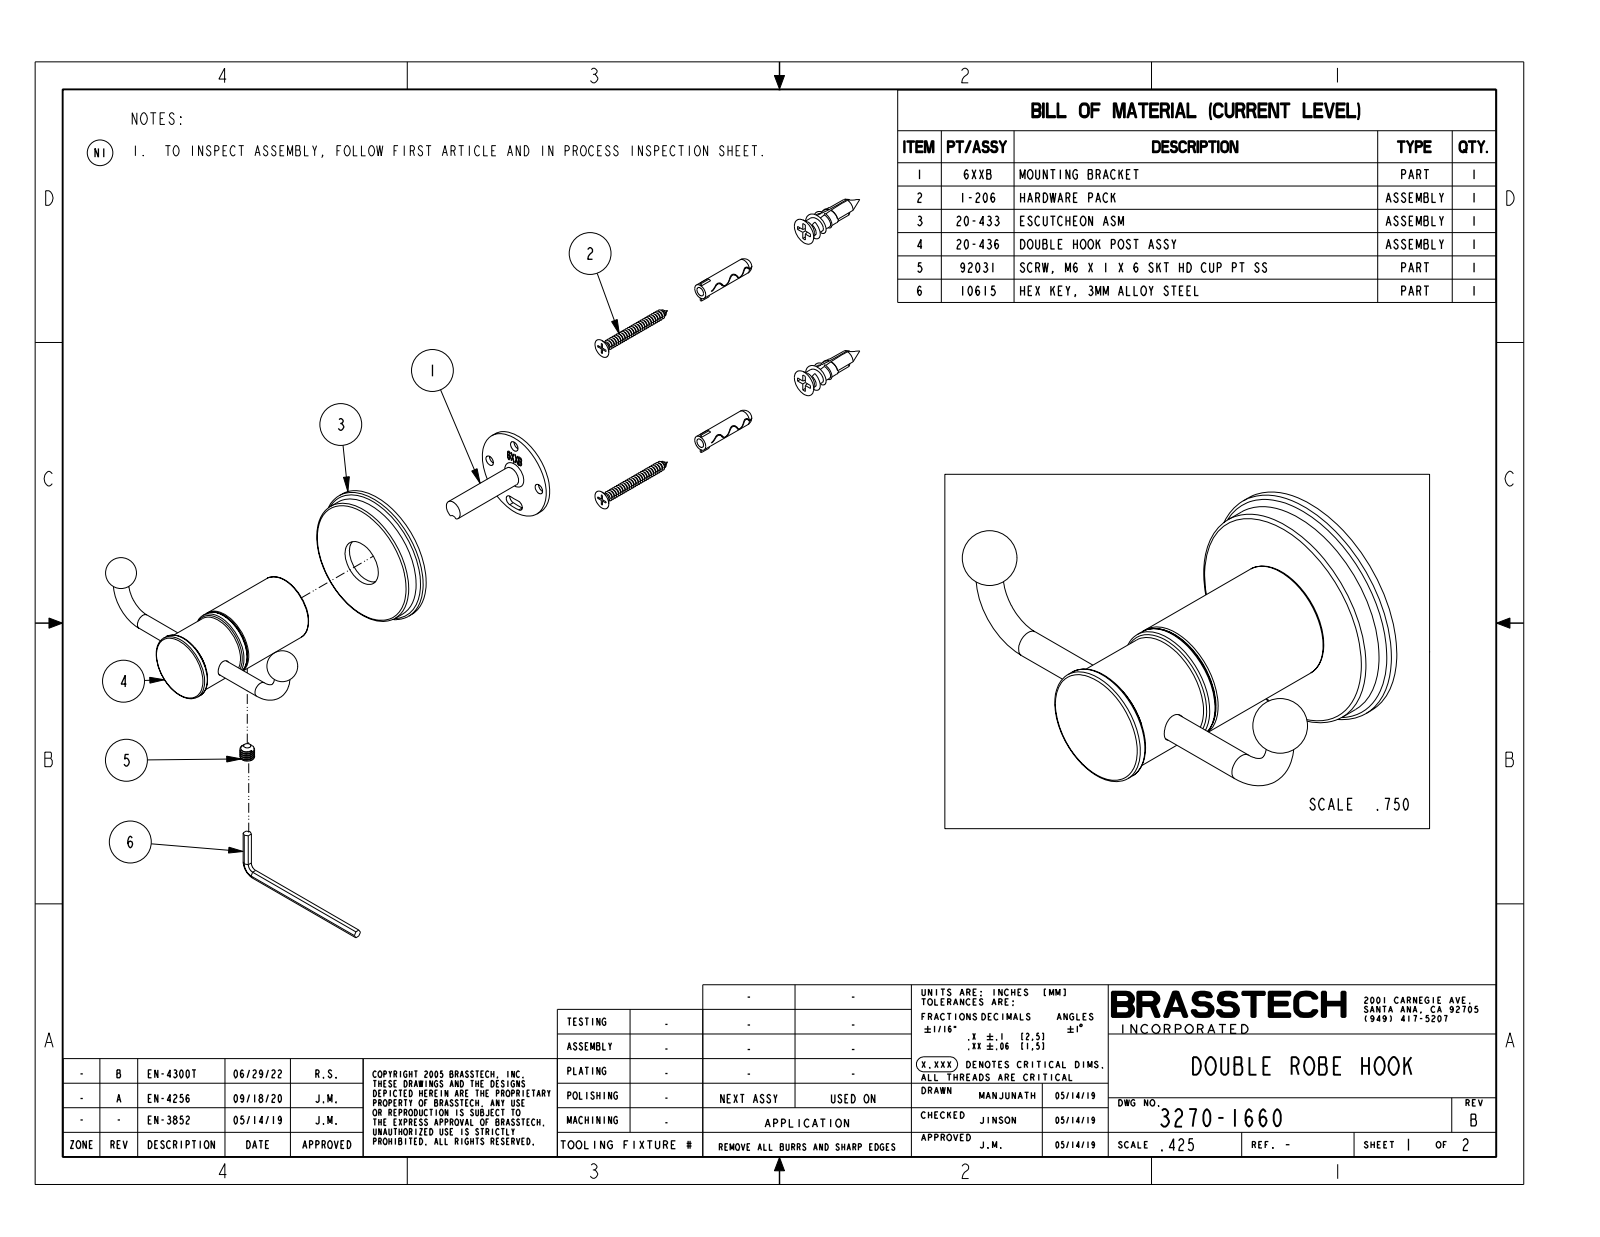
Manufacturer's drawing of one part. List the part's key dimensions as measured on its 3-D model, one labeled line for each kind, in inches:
Part name (STEP PRODUCT): 3270-1660
STEP written by: CREO PARAMETRIC BY PTC INC, 2019352 (CONFIG_CONTROL_DESIGN)
Units: inches
Bodies: 1 solid, 58 faces (6 planar, 16 cylindrical, 36 other)
Overall size (bounding box): 4.266 × 2.77 × 2.25
Volume: 3.736 in³ · Surface area: 23.08 in²
Round bosses / shafts (diameter × count): ⌀2.25 ×1, ⌀2.09 ×1, ⌀1.1 ×1, ⌀1.02 ×1, ⌀0.25 ×1
Main face-to-face distances: 0.35, 2.77, 2.42, 0.36, 2.41
